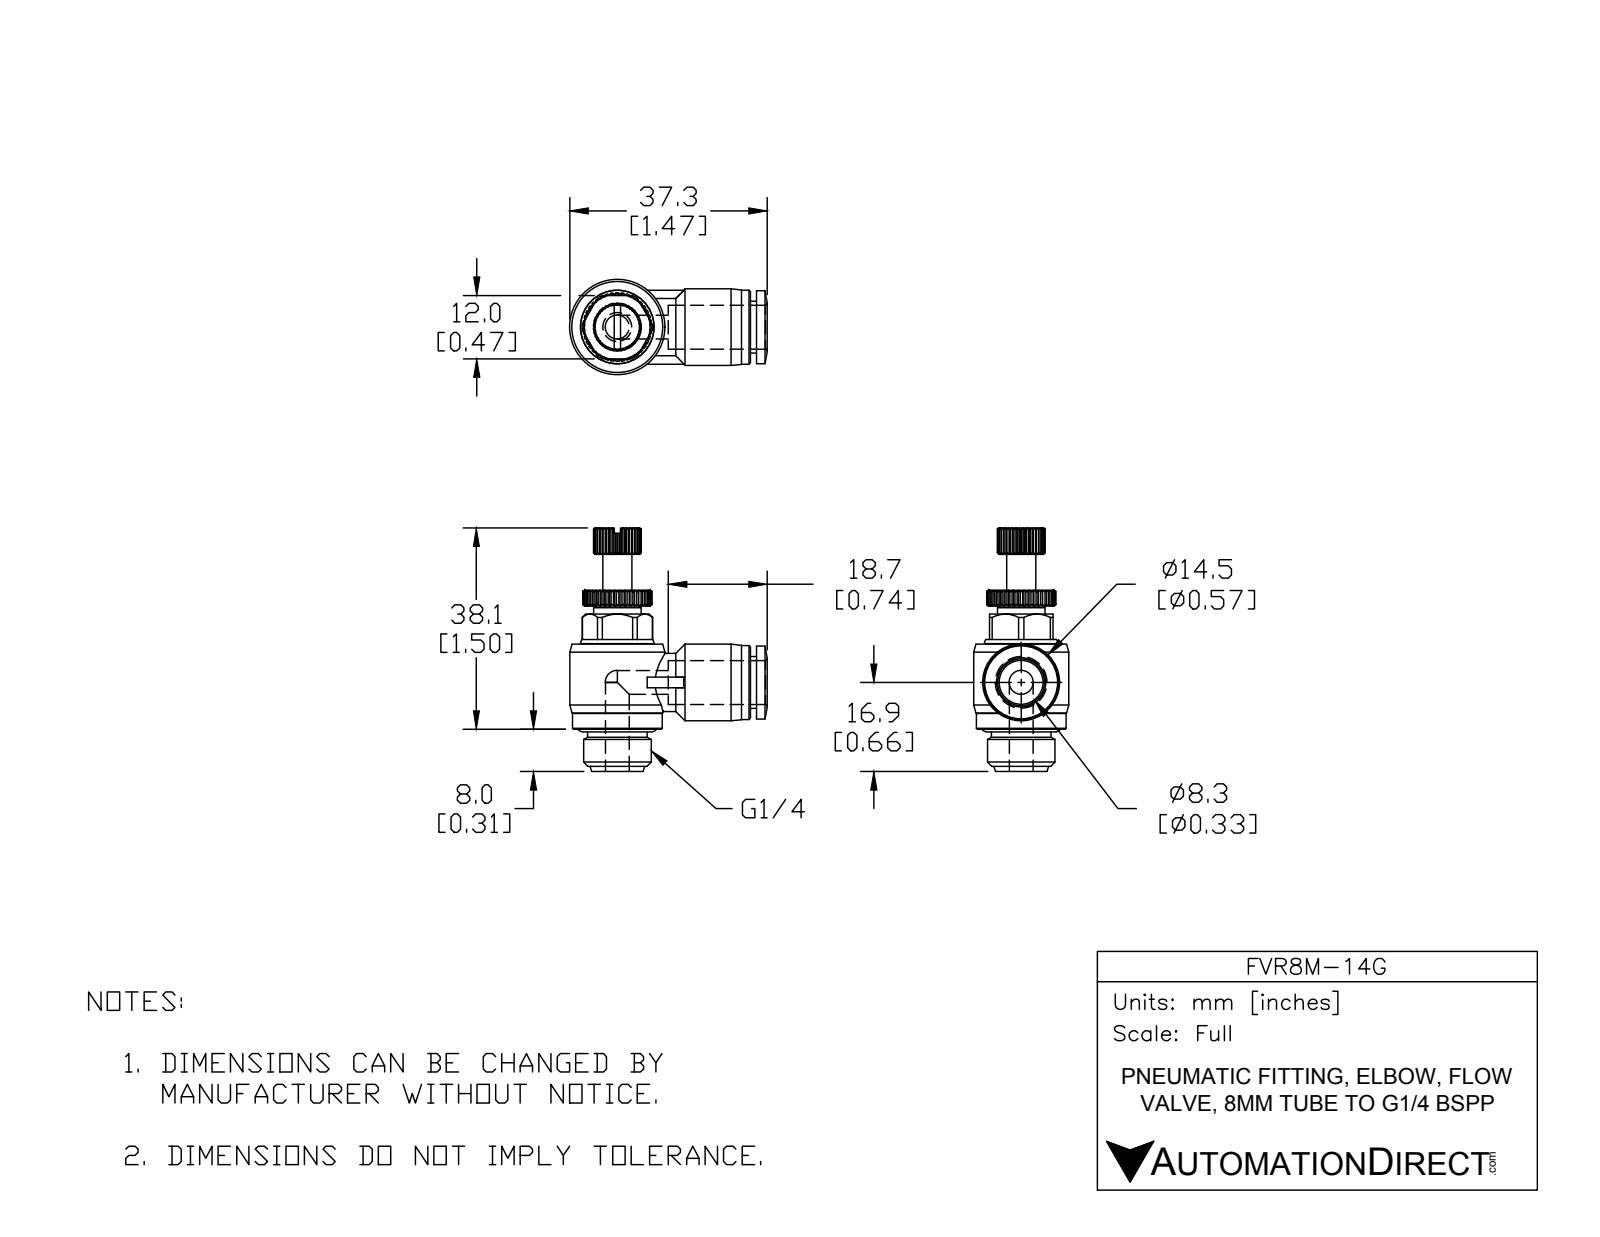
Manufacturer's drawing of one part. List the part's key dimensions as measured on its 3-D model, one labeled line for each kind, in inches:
Part name (STEP PRODUCT): FVR8M-14G
STEP written by: SolidWorks 2015 (AUTOMOTIVE_DESIGN)
Units: inches
Bodies: 2 solids, 515 faces (196 planar, 119 cylindrical, 200 other)
Overall size (bounding box): 1.815 × 1.47 × 0.709
Volume: 0.489 in³ · Surface area: 7.705 in²
Round holes (diameter × count): ⌀0.177 ×2, ⌀0.327 ×1
Round bosses / shafts (diameter × count): ⌀0.709 ×1, ⌀0.669 ×1, ⌀0.583 ×1, ⌀0.571 ×1, ⌀0.551 ×1, ⌀0.543 ×1, ⌀0.528 ×1, ⌀0.504 ×1
Partial cylindrical surfaces — rounded edges, fillets, slot ends (radius × count): R0.256 ×1, R0.262 ×1
Main face-to-face distances: 0.402, 0.512, 0.118, 0.472, 0.234, 0.917, 0.913, 0.516, 0.045, 0.283
